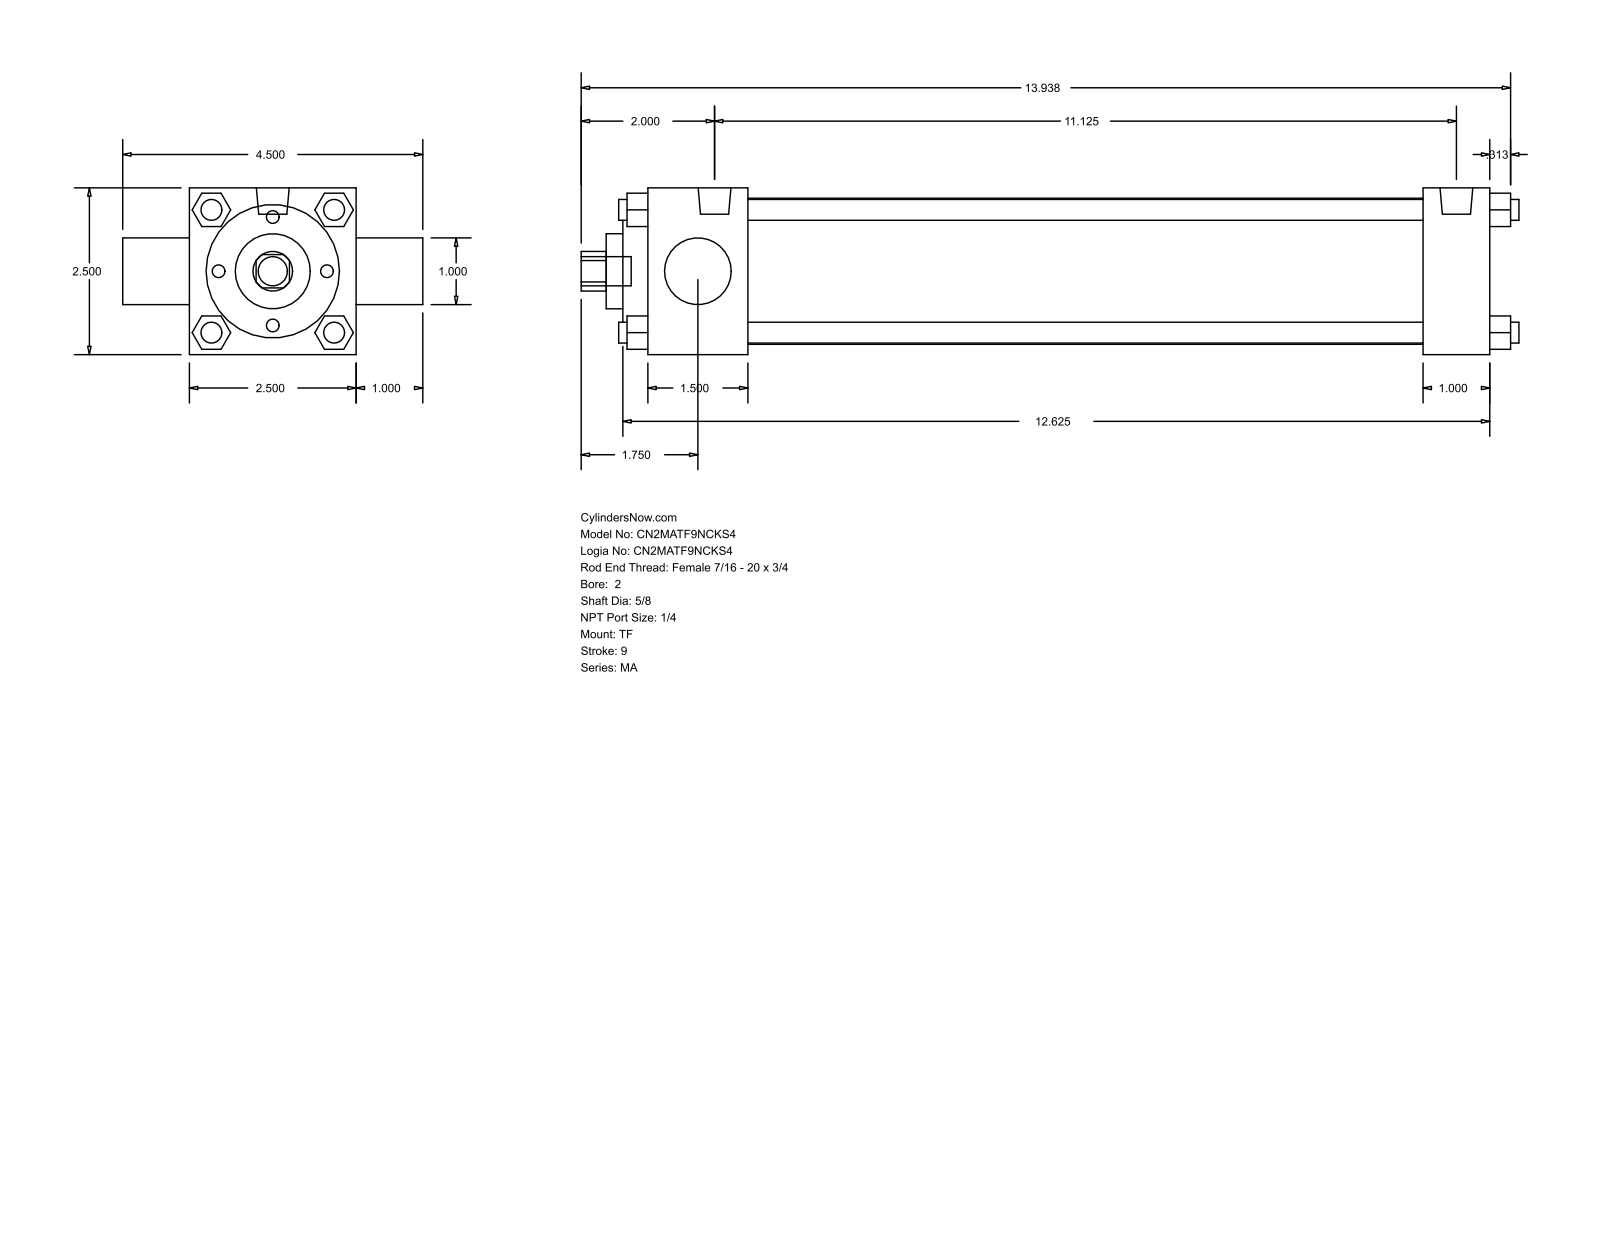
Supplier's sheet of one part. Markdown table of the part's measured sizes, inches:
| quantity | value |
| --- | --- |
| part name | MA_TF__0200_0.625 |
| STEP written by | GSSL Pune (CONFIG_CONTROL_DESIGN) |
| units | inches |
| bodies | 0 solids, 122 faces (93 planar, 29 cylindrical, 0 other) |
| overall size | 14.063 × 4.5 × 2.5 |
| round holes (diameter × count) | 0.625 × 1, 1 × 1, 1.125 × 1, 2 × 1, 2.19 × 1 |
| round bosses / shafts (diameter × count) | 0.313 × 7, 0.492 × 2, 0.437 × 1 |
| partial cylindrical surfaces (radius × count) | 0.297 × 1 |
| main face-to-face distances | 2.5, 1.5, 0.5, 0.375, 12.625, 11.625, 10.125, 11.125, 1, 1.875 |
